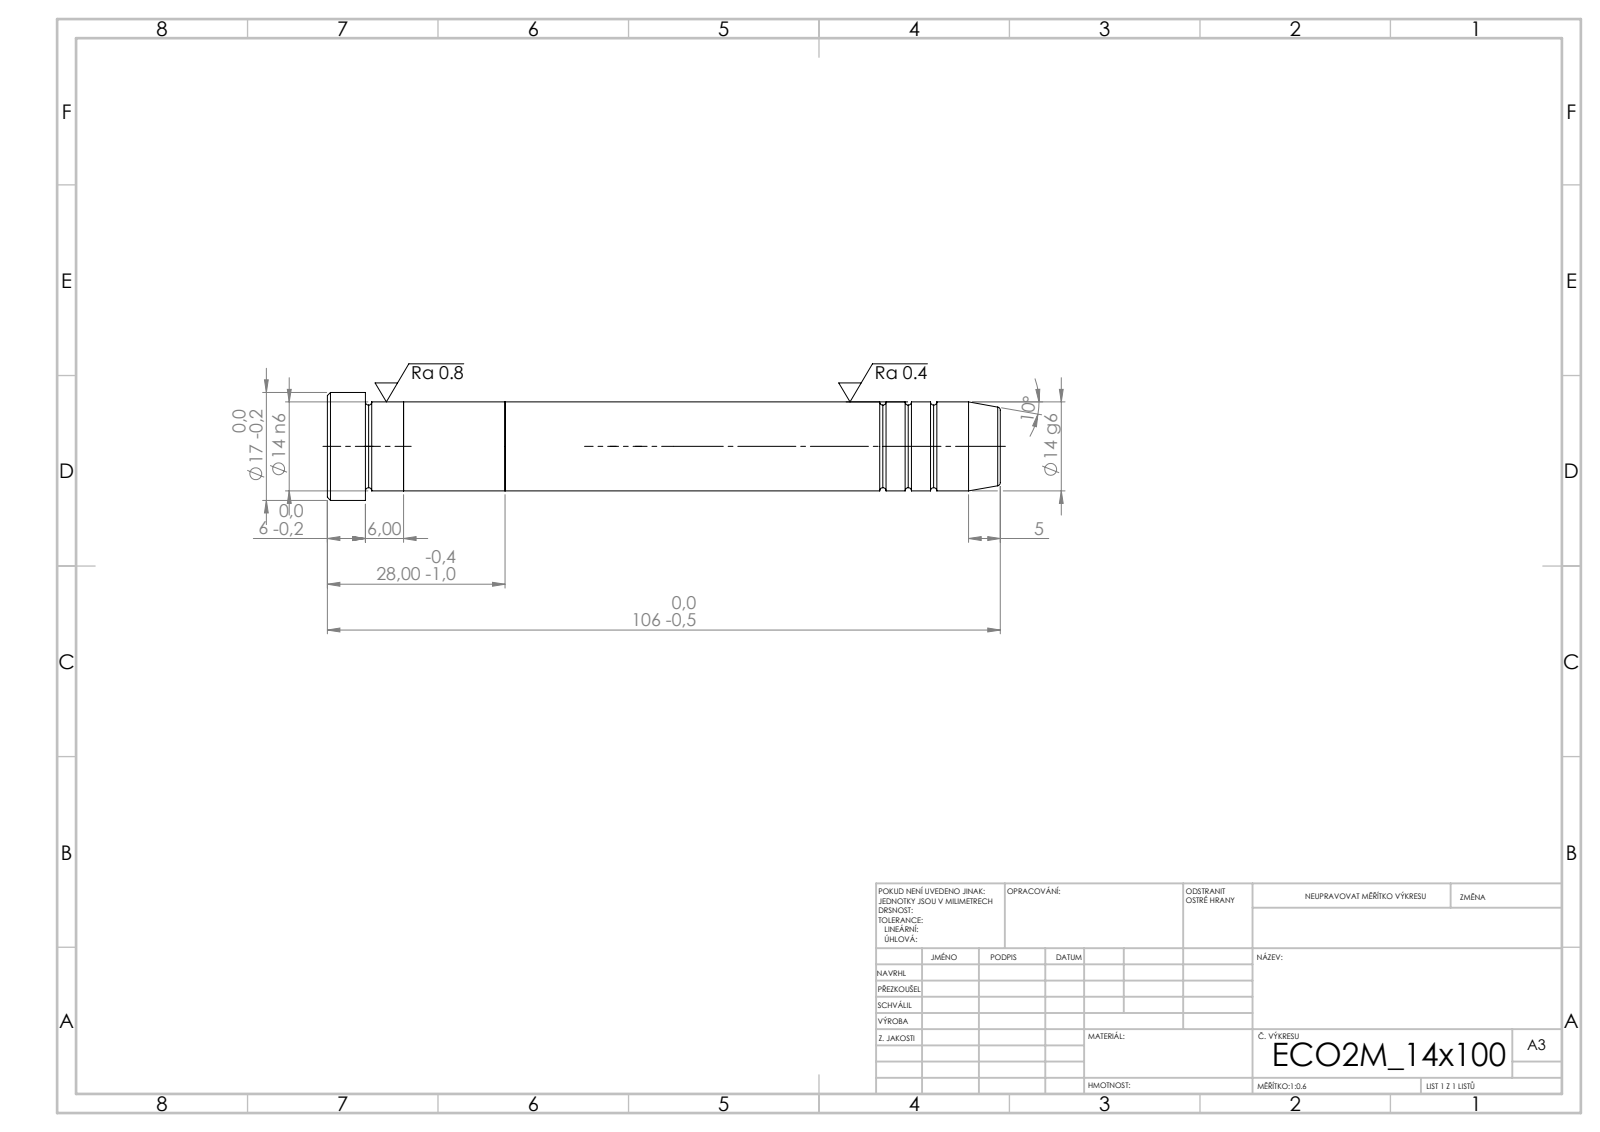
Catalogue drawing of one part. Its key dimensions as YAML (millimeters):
step_written_by: "SolidWorks 2019 (CONFIG_CONTROL_DESIGN)"
units: millimeters
bodies: {solids: 3, faces: 43, planar: 7, cylindrical: 14, other: 22}
overall_size: [106, 17, 17]
volume: 16588
surface_area: 5808
round_bosses_or_shafts:
  - {diameter: 17, count: 1}
  - {diameter: 14, count: 1}
face_to_face_distances: [16, 28, 12, 6, 78, 94, 106, 100, 22]
